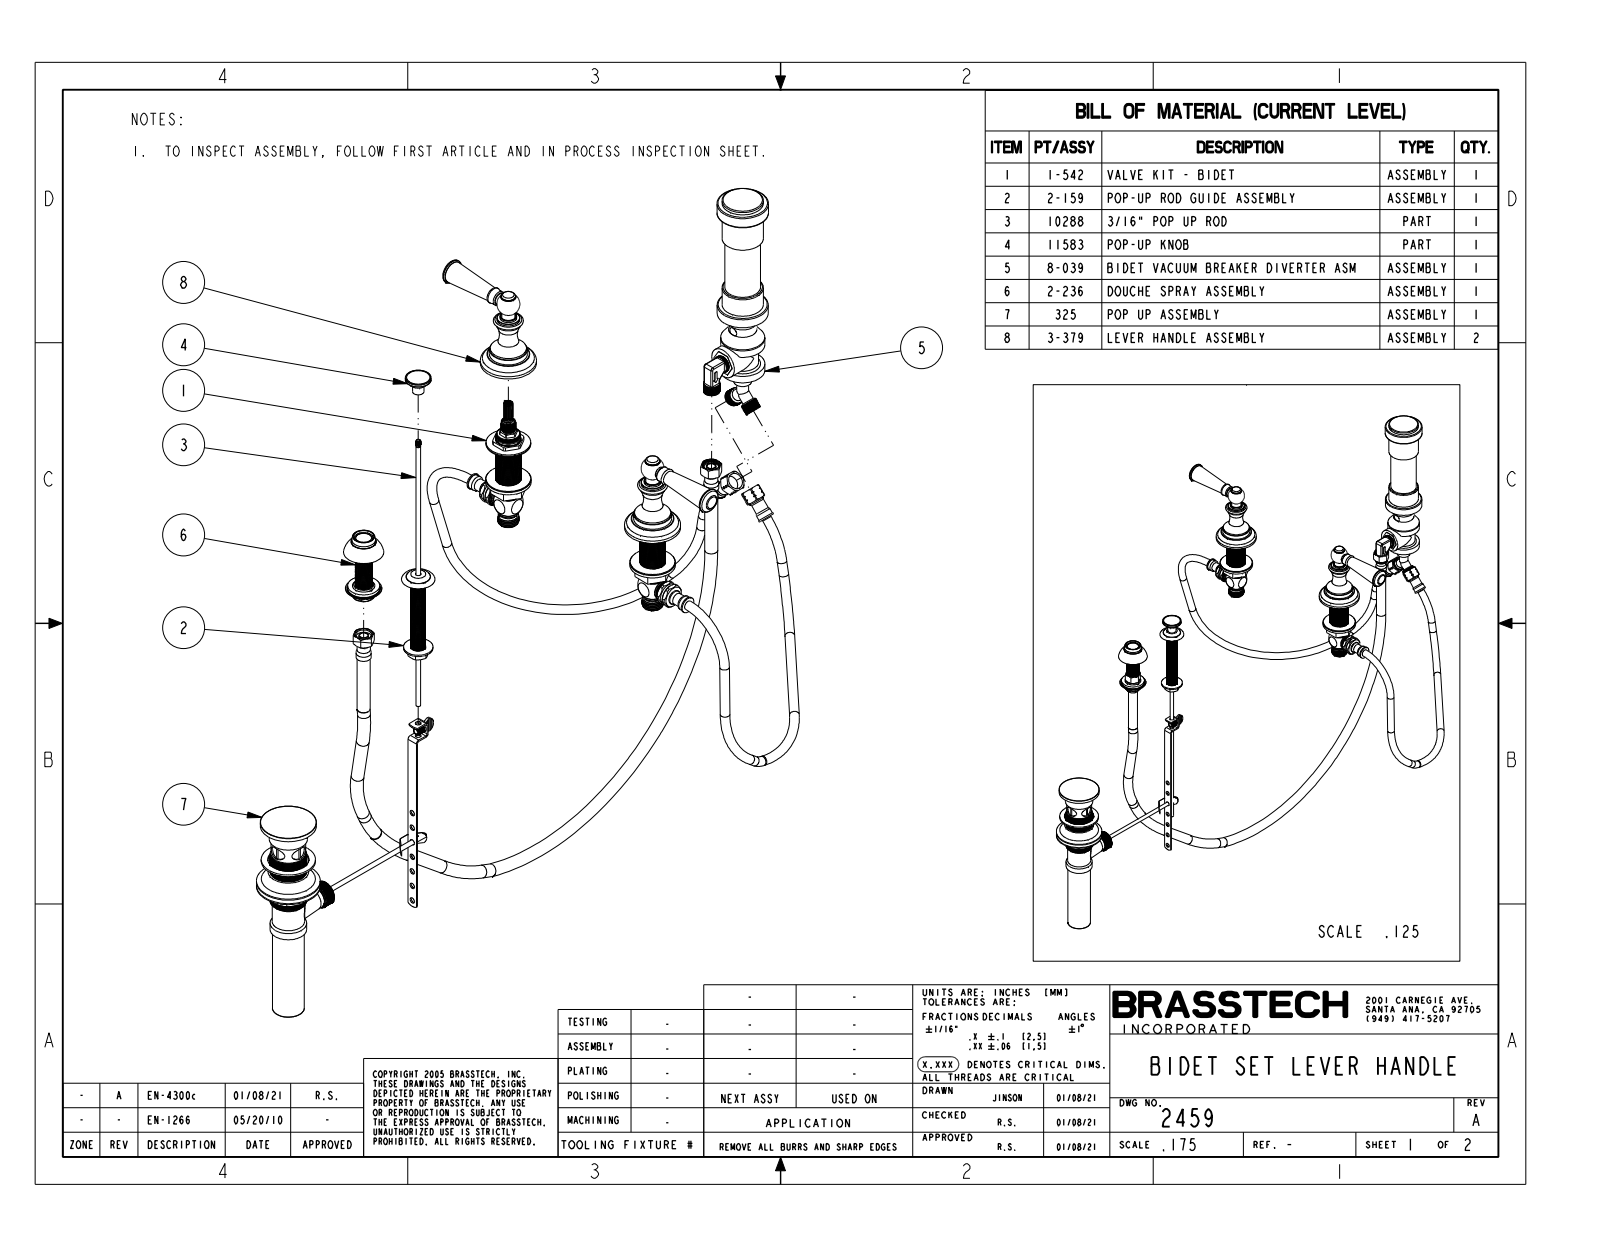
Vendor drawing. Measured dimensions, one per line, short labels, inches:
name: 2459
written by: CREO PARAMETRIC BY PTC INC, 2018400 (CONFIG_CONTROL_DESIGN)
unit: in
bodies: 5 solids, 269 faces (67 planar, 70 cylindrical, 132 other)
size: 22.798 × 14.6 × 5.445
volume: 21.3 in³; area: 99.66 in²
holes: 1× ⌀0.625, 1× ⌀0.792, 1× ⌀0.94
bosses: 2× ⌀2.2, 2× ⌀1.49, 2× ⌀1.42, 2× ⌀0.9, 2× ⌀0.66, 2× ⌀0.56, 2× ⌀0.517, 1× ⌀2.02
rounds: 1× R0.357
face distances: 5.445, 0.5, 5.295, 0.15, 4.795, 0.65, 0.42, 4.375, 4.875, 5.025
